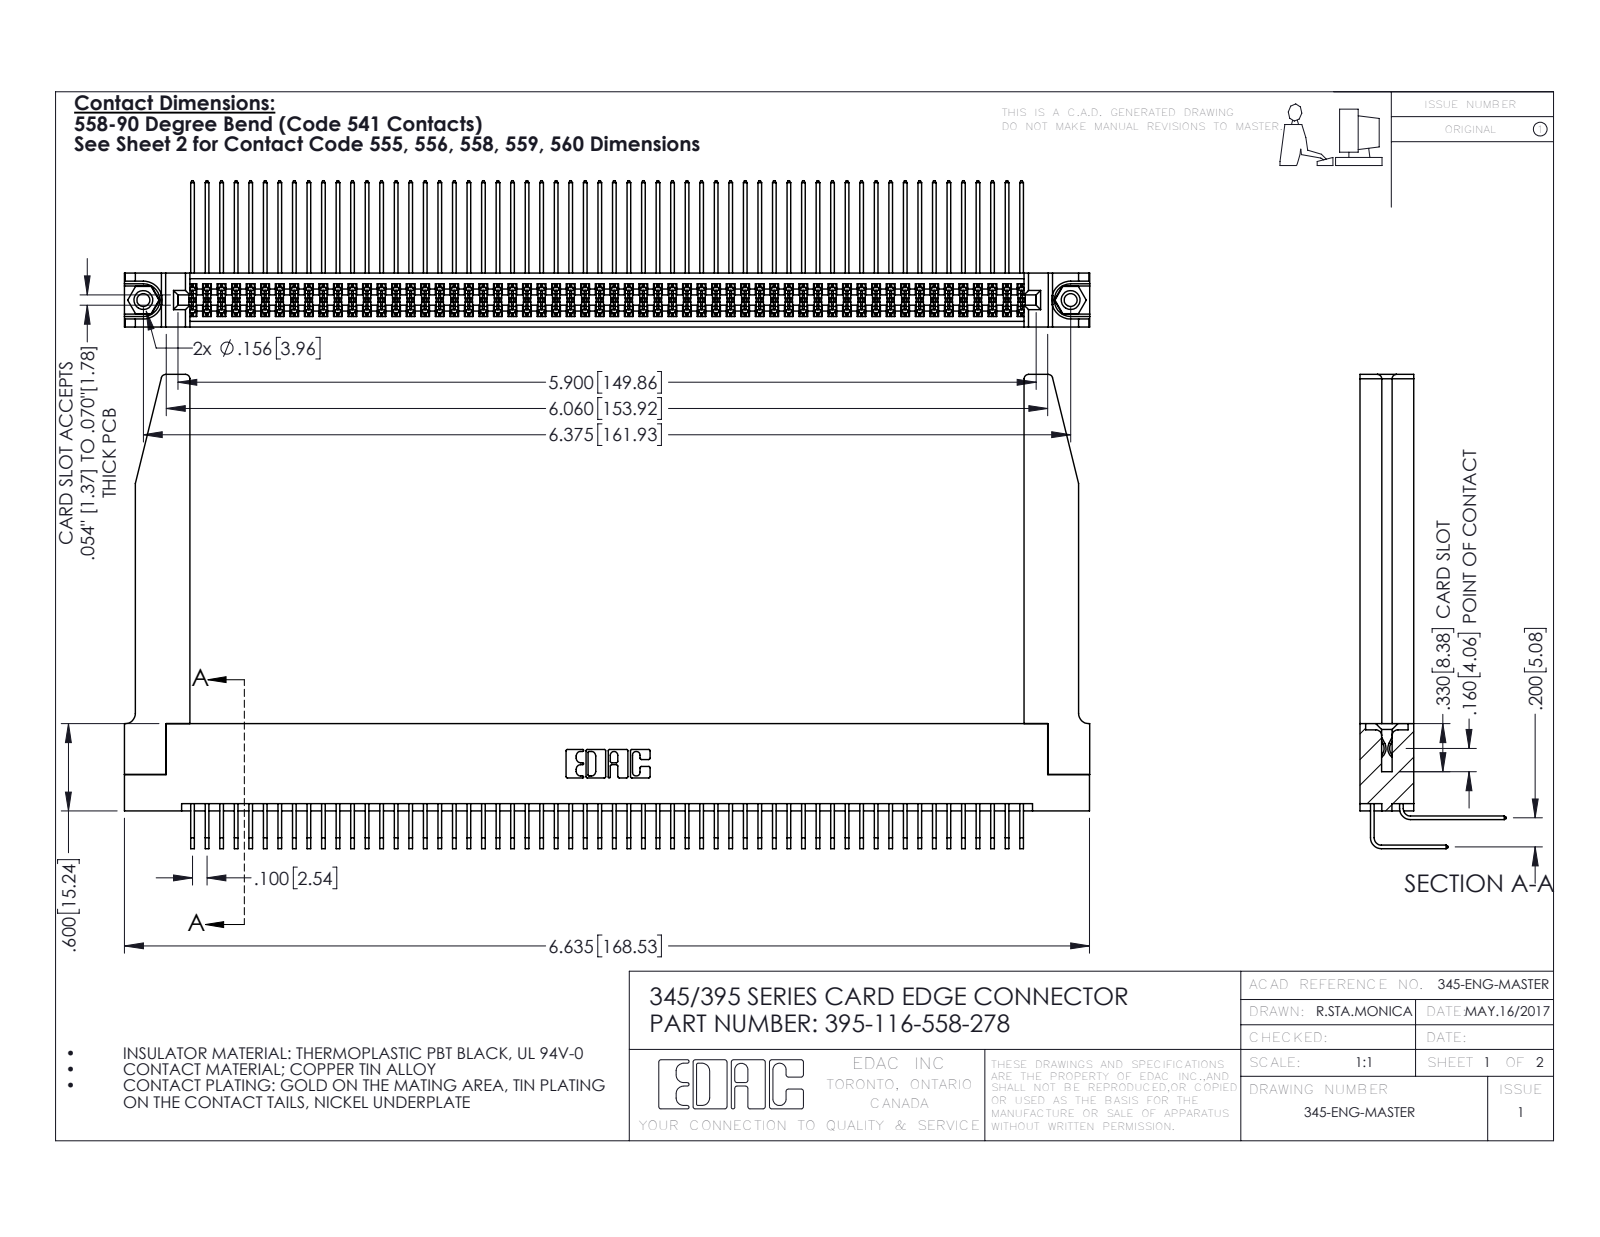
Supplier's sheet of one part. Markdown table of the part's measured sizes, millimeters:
| quantity | value |
| --- | --- |
| part name | 345-250-001_345-250-001-102; 345-292-001_558 559 Tail - 1; 395-116-558-278; 345-292-001_558 Tail - 2 (+2 more) |
| STEP written by | SolidWorks 2016 (CONFIG_CONTROL_DESIGN) |
| units | millimeters |
| bodies | 121 solids, 6392 faces (4282 planar, 2058 cylindrical, 52 other) |
| overall size | 168.6 × 82.8 × 25.5 |
| volume | 24 960 mm³ |
| surface area | 35 710 mm² |
| round holes (diameter × count) | 2.3 × 2, 3.2 × 2, 4 × 2, 1.6 × 1 |
| round bosses / shafts (diameter × count) | 3.9 × 2 |
| partial cylindrical surfaces (radius × count) | 0.2 × 174, 0.3 × 22, 0.8 × 8, 0.2 × 6, 0.8 × 6, 0.7 × 3, 0.4 × 2, 0.5 × 2 |
| main face-to-face distances | 1.8, 7.6, 9.4, 5.1, 2.5, 6.9, 0.6, 5.7, 0.6, 7.2 |
| hole center spacings | 6.9, 155.9, 161.9 |
